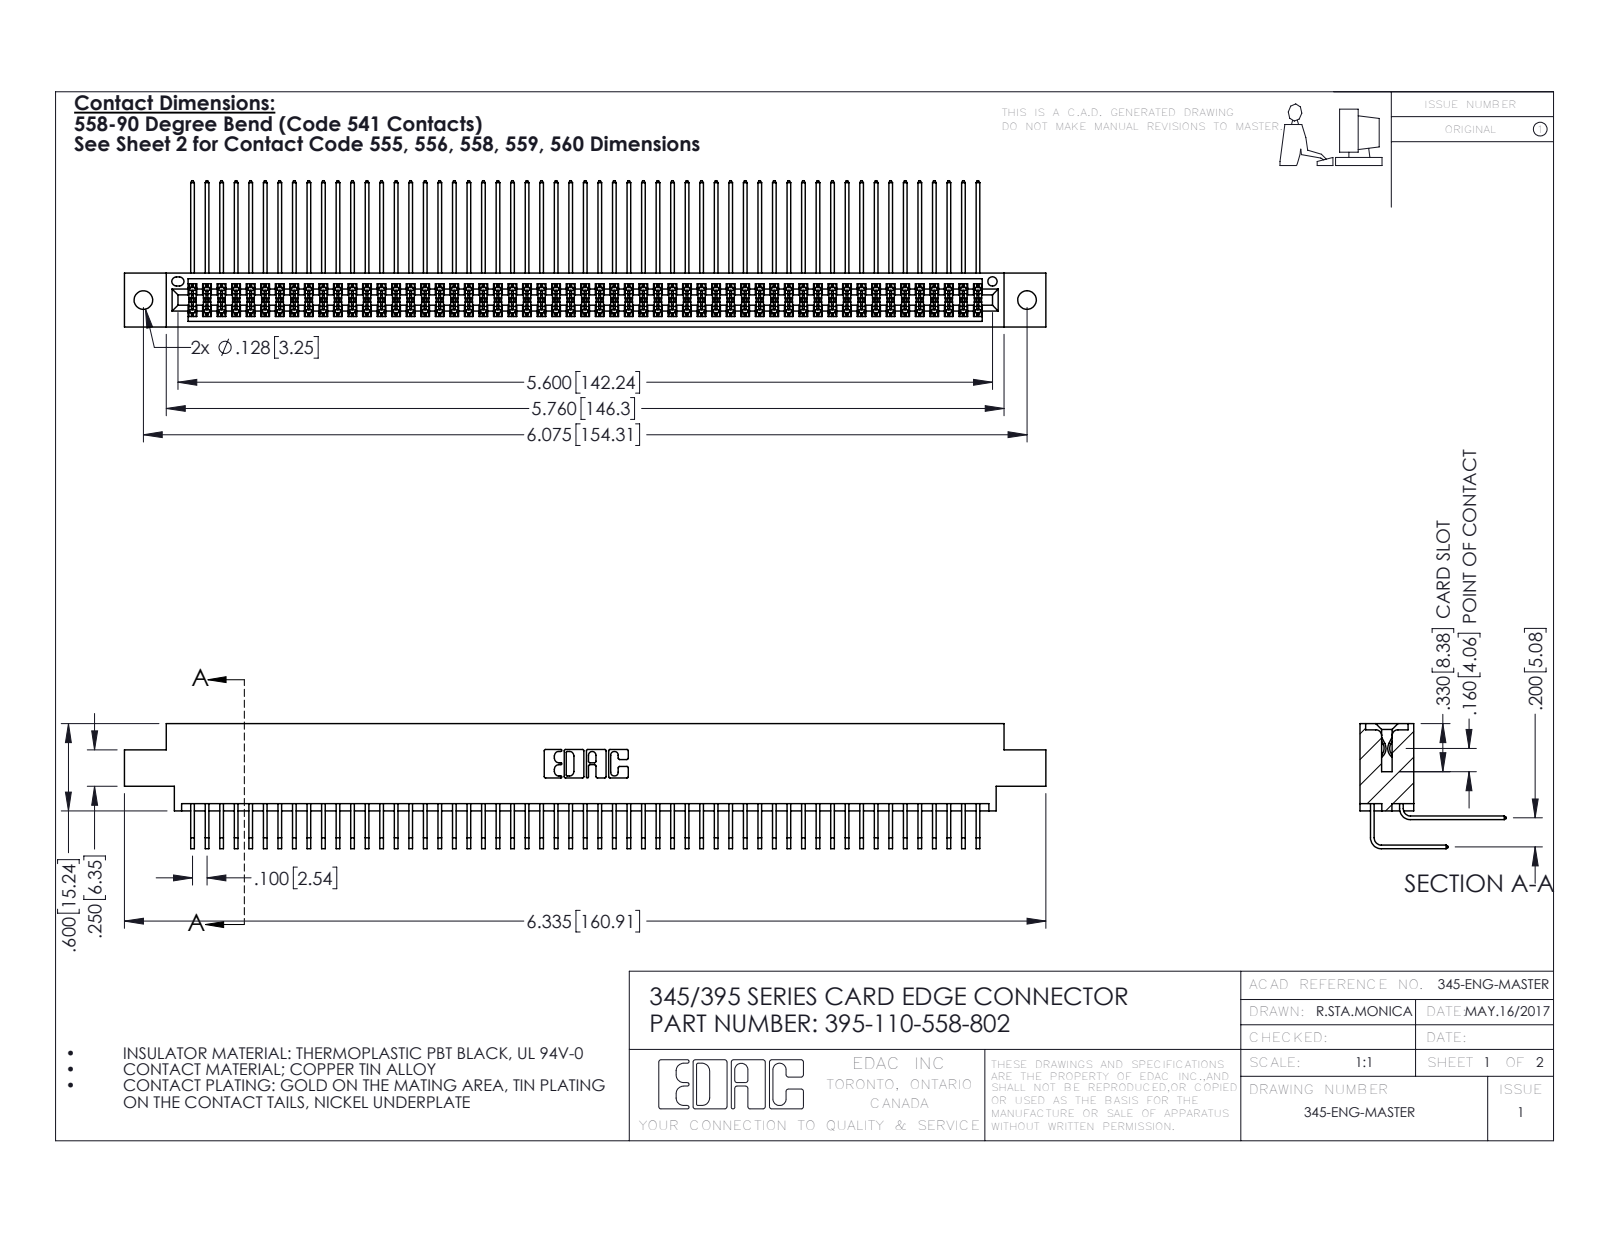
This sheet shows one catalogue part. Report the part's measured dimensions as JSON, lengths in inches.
{"part_name": "345-292-001_558 559 Tail - 1; 395-110-558-802; 345 Part_0.170 Offset - 0.128 Dia; 345-292-001_558 Tail - 2", "step_written_by": "SolidWorks 2016 (CONFIG_CONTROL_DESIGN)", "units": "inches", "bodies": {"solids": 111, "faces": 5850, "planar": 3934, "cylindrical": 1916, "other": 0}, "overall_size": [6.335, 1.005, 0.859], "volume_in3": 0.991, "surface_area_in2": 42.01, "round_holes": [[0.128, 2], [0.064, 1]], "partial_cylinders_radius": [[0.006, 165], [0.01, 22], [0.007, 6], [0.031, 6], [0.026, 3], [0.014, 2], [0.019, 2], [0.022, 2]], "face_to_face_distances": [0.072, 0.298, 0.2, 0.37, 0.098, 0.272, 0.025, 0.225, 0.175, 0.025], "hole_center_spacings": [0.27, 5.839, 6.075]}
